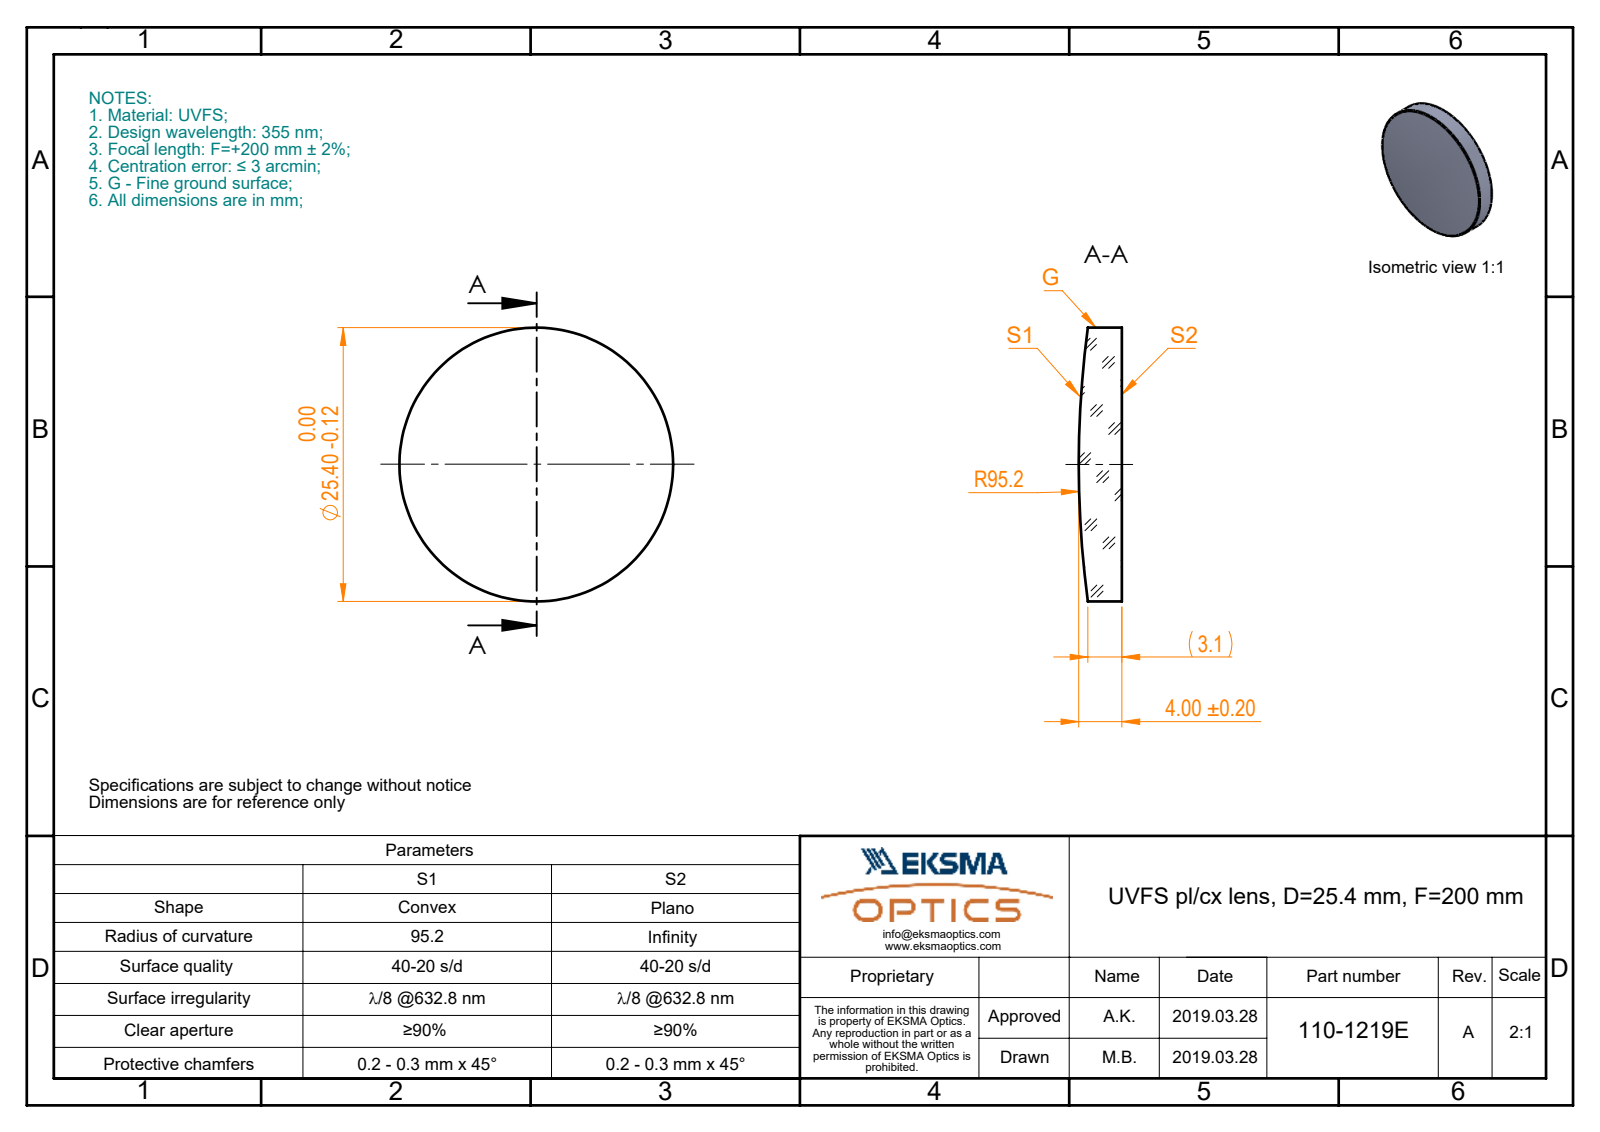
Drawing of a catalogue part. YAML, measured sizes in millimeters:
part_name: "110-1219E UVFS pl-cx 25.4 F200"
step_written_by: "SolidWorks 2017 (CONFIG_CONTROL_DESIGN)"
units: millimeters
bodies: {solids: 1, faces: 5, planar: 1, cylindrical: 2, other: 2}
overall_size: [25.4, 25.4, 4]
volume: 1812
surface_area: 1267
round_bosses_or_shafts:
  - {diameter: 25.4, count: 1}
